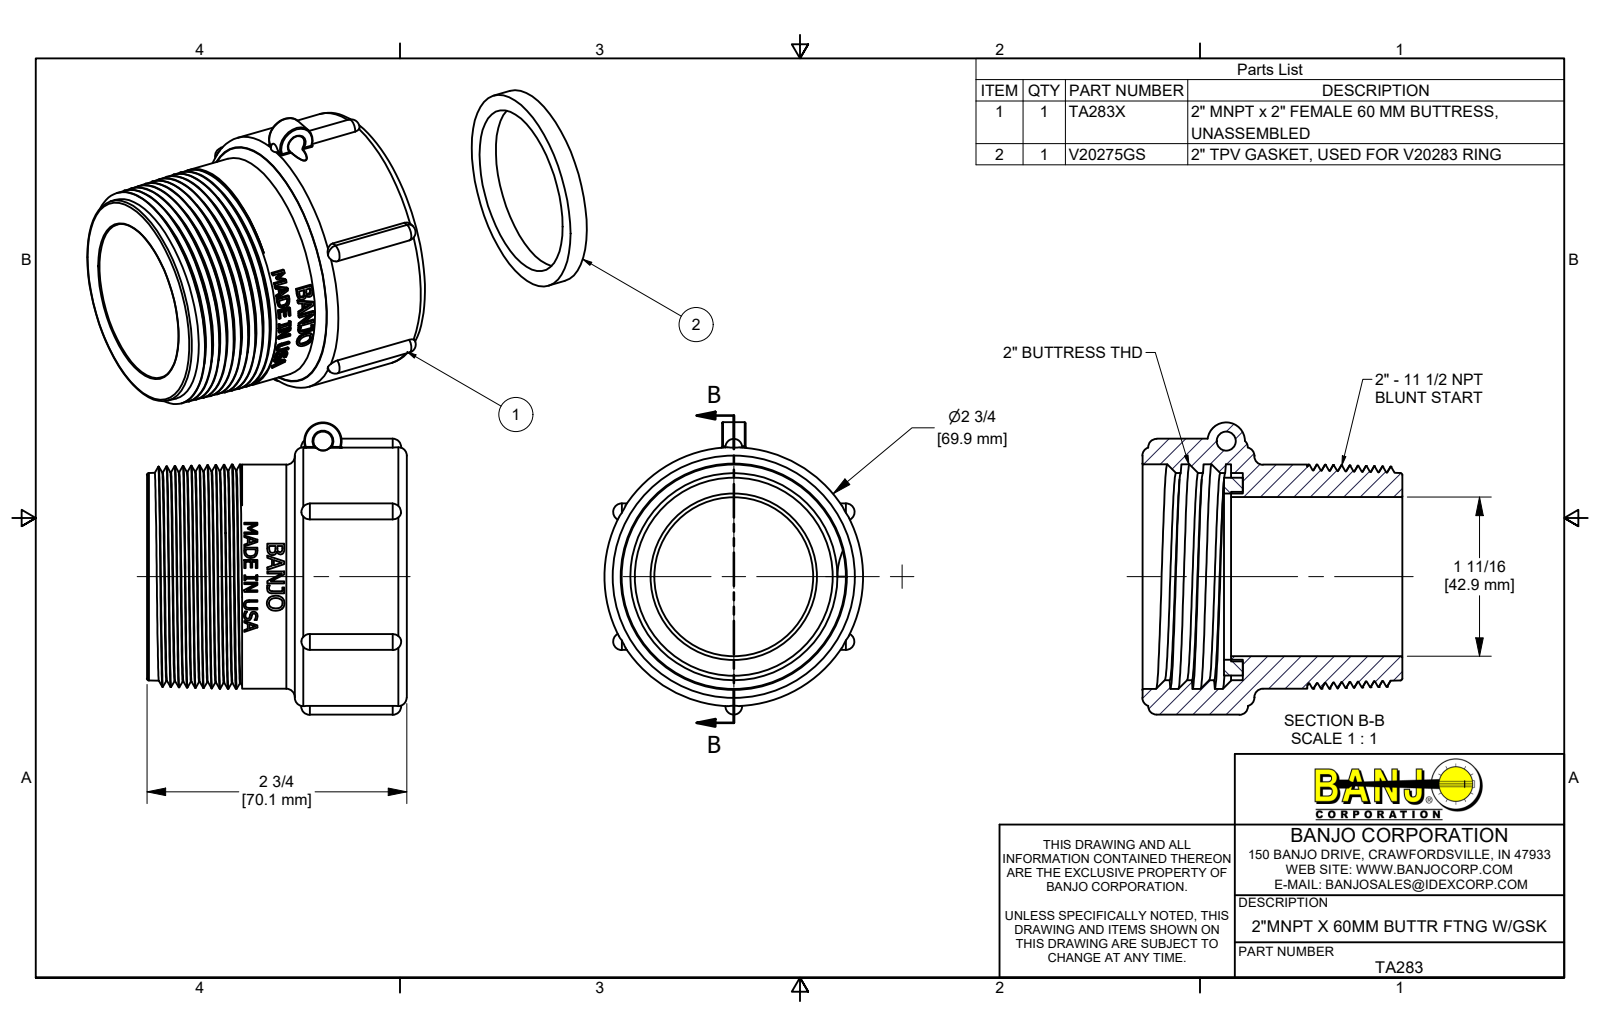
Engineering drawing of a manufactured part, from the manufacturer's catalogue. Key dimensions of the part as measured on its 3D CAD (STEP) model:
Part name (STEP PRODUCT): TA283; TA283X; V20275GS
STEP written by: Autodesk Inventor 2022 (AUTOMOTIVE_DESIGN)
Units: inches
Bodies: 2 solids, 416 faces (167 planar, 73 cylindrical, 176 other)
Overall size (bounding box): 3.105 × 2.76 × 2.75
Volume: 5.774 in³ · Surface area: 59.56 in²
Round holes (diameter × count): ⌀0.2 ×1, ⌀1.69 ×1, ⌀1.765 ×1, ⌀2.2 ×1, ⌀2.385 ×1
Round bosses / shafts (diameter × count): ⌀2.75 ×1, ⌀2.38 ×1, ⌀2.1 ×1, ⌀1.8 ×1
Partial cylindrical surfaces — rounded edges, fillets, slot ends (radius × count): R0.09 ×10, R0.01 ×2, R0.2 ×1, R0.616 ×1, R0.689 ×1, R1.21 ×1
Main face-to-face distances: 1.695, 0.2, 1.895, 0.075, 0.125, 1.82, 0.865, 0.94, 1.065, 2.76
